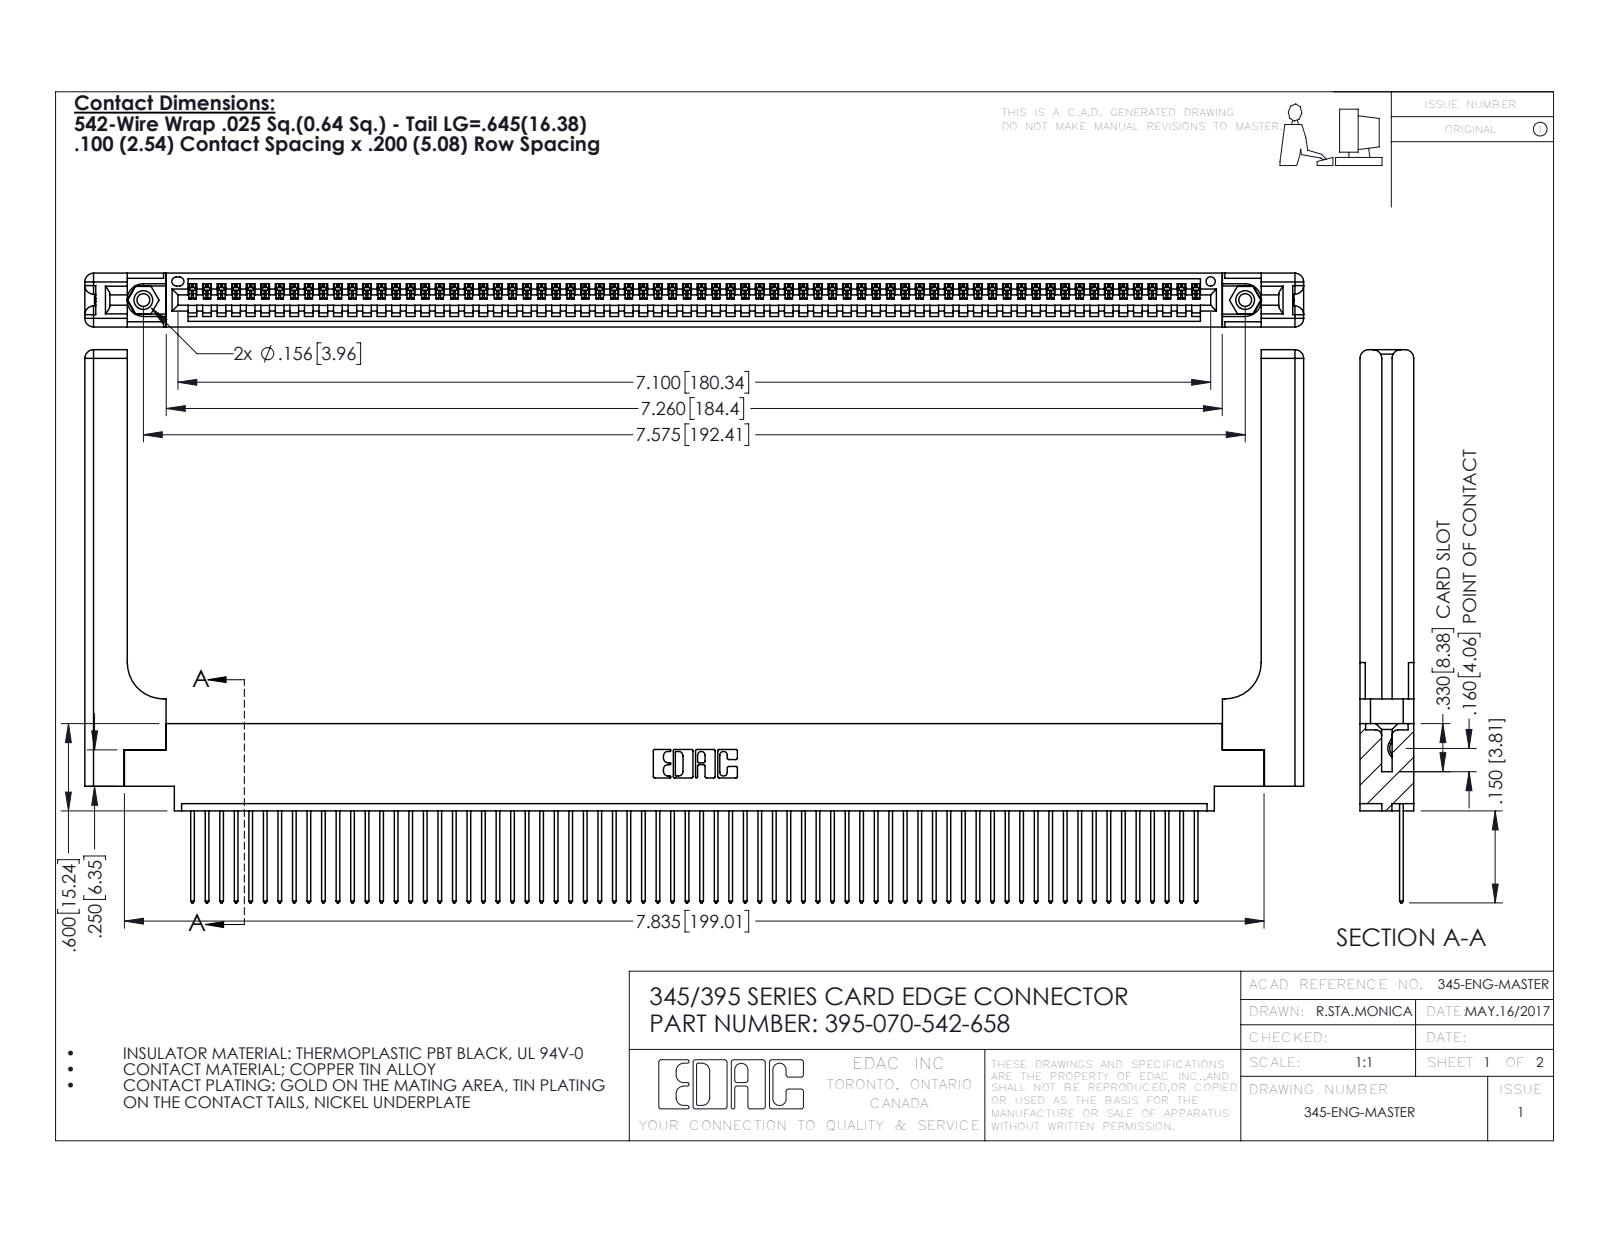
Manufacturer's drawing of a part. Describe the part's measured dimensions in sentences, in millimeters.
The part is named "345-250-001_345-250-001-102; 345-220-058_345-220-058; 345-292-001_345-293-142; 395-070-542-658 (+1 more)". Its 3-D file was written by "SolidWorks 2016 (CONFIG_CONTROL_DESIGN)". It is 75 solids with 4446 faces: 3032 planar, 1354 cylindrical and 60 other. Overall it measures 212.8 by 96.6 by 9.4 millimeters. Its volume is 28 990 cubic millimeters and its surface area 34 020 square millimeters. Round holes: 2 of diameter 2.3, 2 of diameter 3.2, 2 of diameter 4, 1 of diameter 1.6. Round bosses or shafts: 2 of diameter 3.9. Partial cylindrical surfaces (rounded edges, fillets, slot ends): 140 of radius 0.2, 140 of radius 0.3, 22 of radius 0.3, 16 of radius 1.5, 6 of radius 0.2, 6 of radius 0.8, 3 of radius 0.7, 2 of radius 0.8. The main face-to-face distances are 1.8, 7.6, 9.4, 2.5, 6.9, 0.6, 5.1, 5.7, 3.8, 3.8. The hole center spacings are 6.9, 186.4, 192.4.
